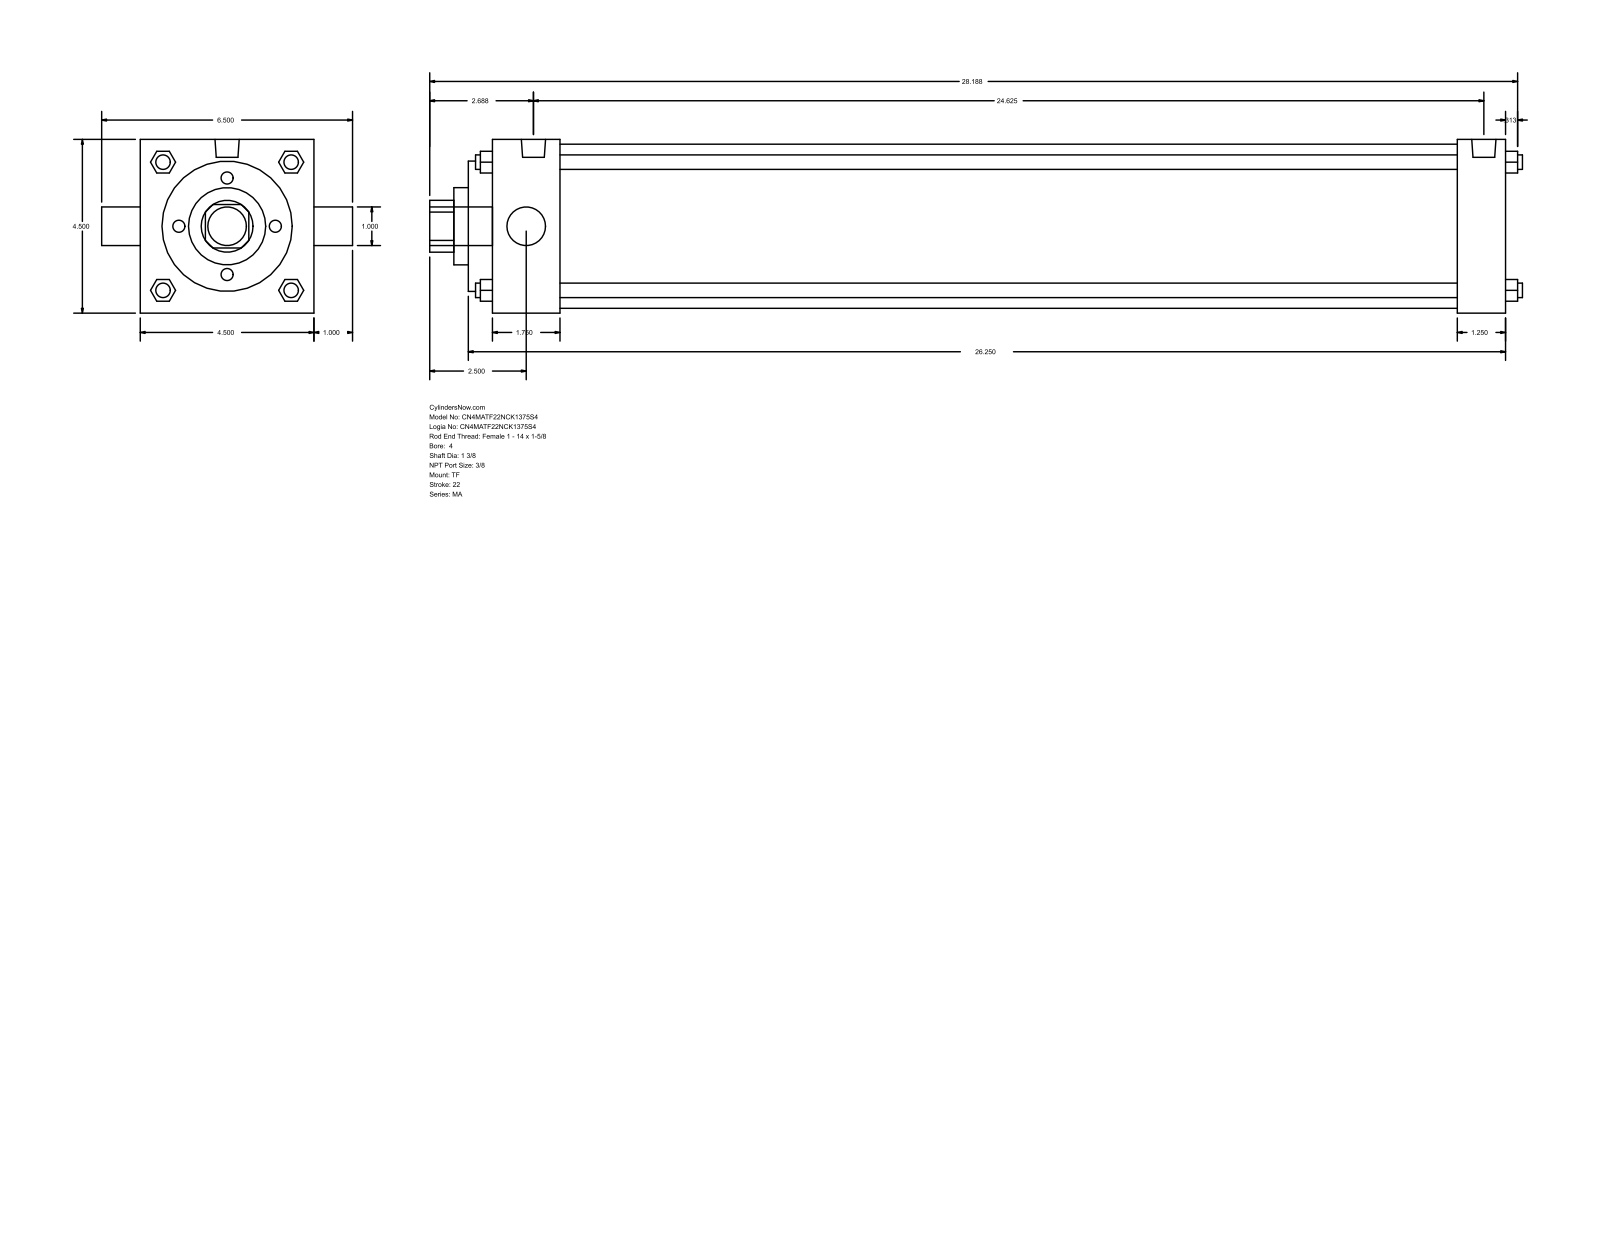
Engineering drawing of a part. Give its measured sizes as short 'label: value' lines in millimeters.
name: MA_TF__0400_1.375
written by: GSSL Pune (CONFIG_CONTROL_DESIGN)
unit: mm
bodies: 0 solids, 122 faces (93 planar, 29 cylindrical, 0 other)
size: 719.14 × 165.1 × 114.3
holes: 1× ⌀25.4, 1× ⌀34.92, 1× ⌀50.8, 1× ⌀85.72, 1× ⌀107.95
bosses: 4× ⌀9.53, 3× ⌀11.11, 2× ⌀15.93, 1× ⌀25.4
rounds: 1× R17.06
face distances: 114.3, 666.75, 682.62, 15.87, 650.87, 635, 31.75, 60.32, 44.45, 590.55
